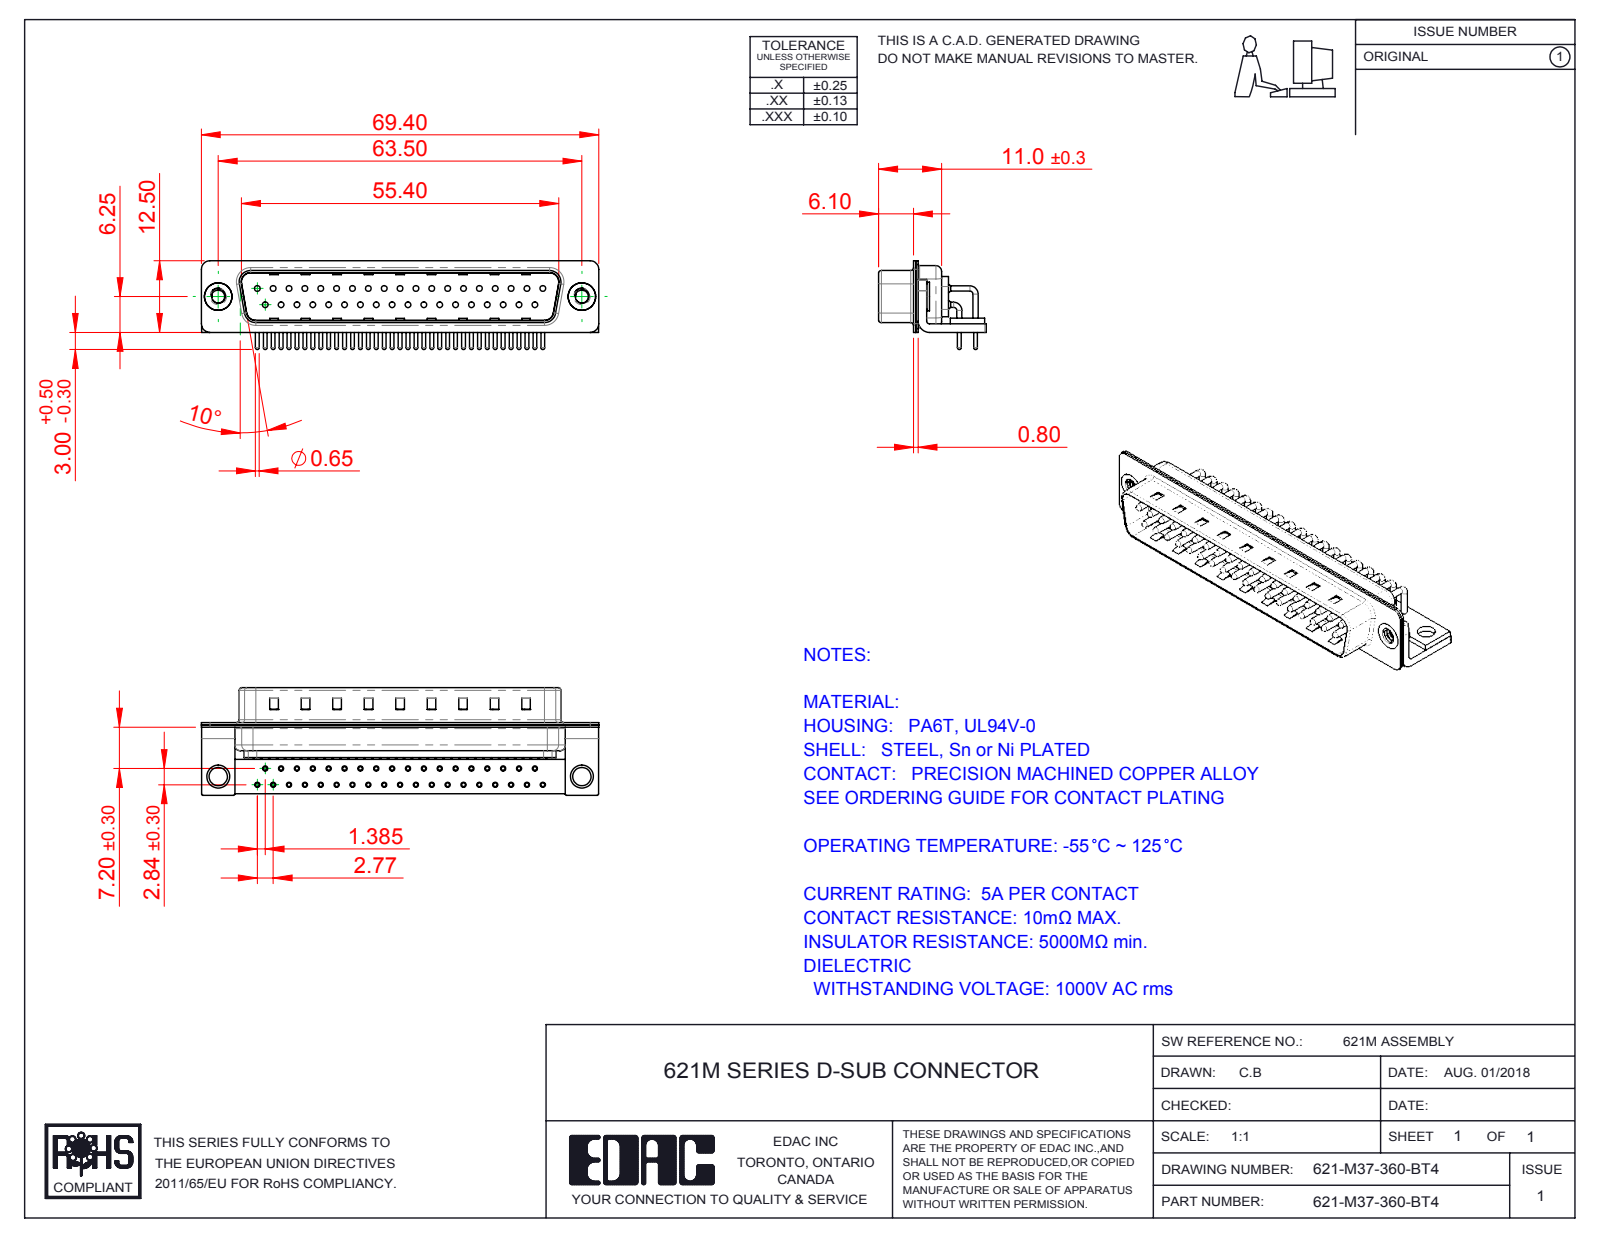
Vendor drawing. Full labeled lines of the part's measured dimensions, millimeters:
Part name (STEP PRODUCT): 621M Contact Row 2; 621M Contact Row 1; 621M 4-40 Threaded Rivet_Stabilizer; 621M Shell Front_37 Contacts (+5 more)
STEP written by: SolidWorks 2016 (CONFIG_CONTROL_DESIGN)
Units: millimetres
Bodies: 45 solids, 4606 faces (2597 planar, 1569 cylindrical, 440 other)
Overall size (bounding box): 69.4 × 18.8 × 15.49
Volume: 4 597 mm³ · Surface area: 11 912 mm²
Round holes (diameter × count): ⌀0.9 ×37, ⌀1 ×37, ⌀1.7 ×37, ⌀2 ×37, ⌀2.26 ×2, ⌀3.2 ×2, ⌀4 ×2, ⌀4.8 ×2
Round bosses / shafts (diameter × count): ⌀0.9 ×46, ⌀1.5 ×37, ⌀0.65 ×37, ⌀5 ×2, ⌀4.9 ×2
Partial cylindrical surfaces — rounded edges, fillets, slot ends (radius × count): R1.01 ×37, R0.25 ×16, R1.5 ×16, R2 ×13, R0.5 ×9, R1.6 ×8, R0.6 ×4, R0.65 ×4
Main face-to-face distances: 0.4, 0.85, 1.25, 9.55, 1.5, 10.4, 8.3, 0.8, 8.7, 1
Hole centre spacings: 3.16, 2.77, 5.54, 8.31, 11.08, 13.85, 5.03, 16.62
